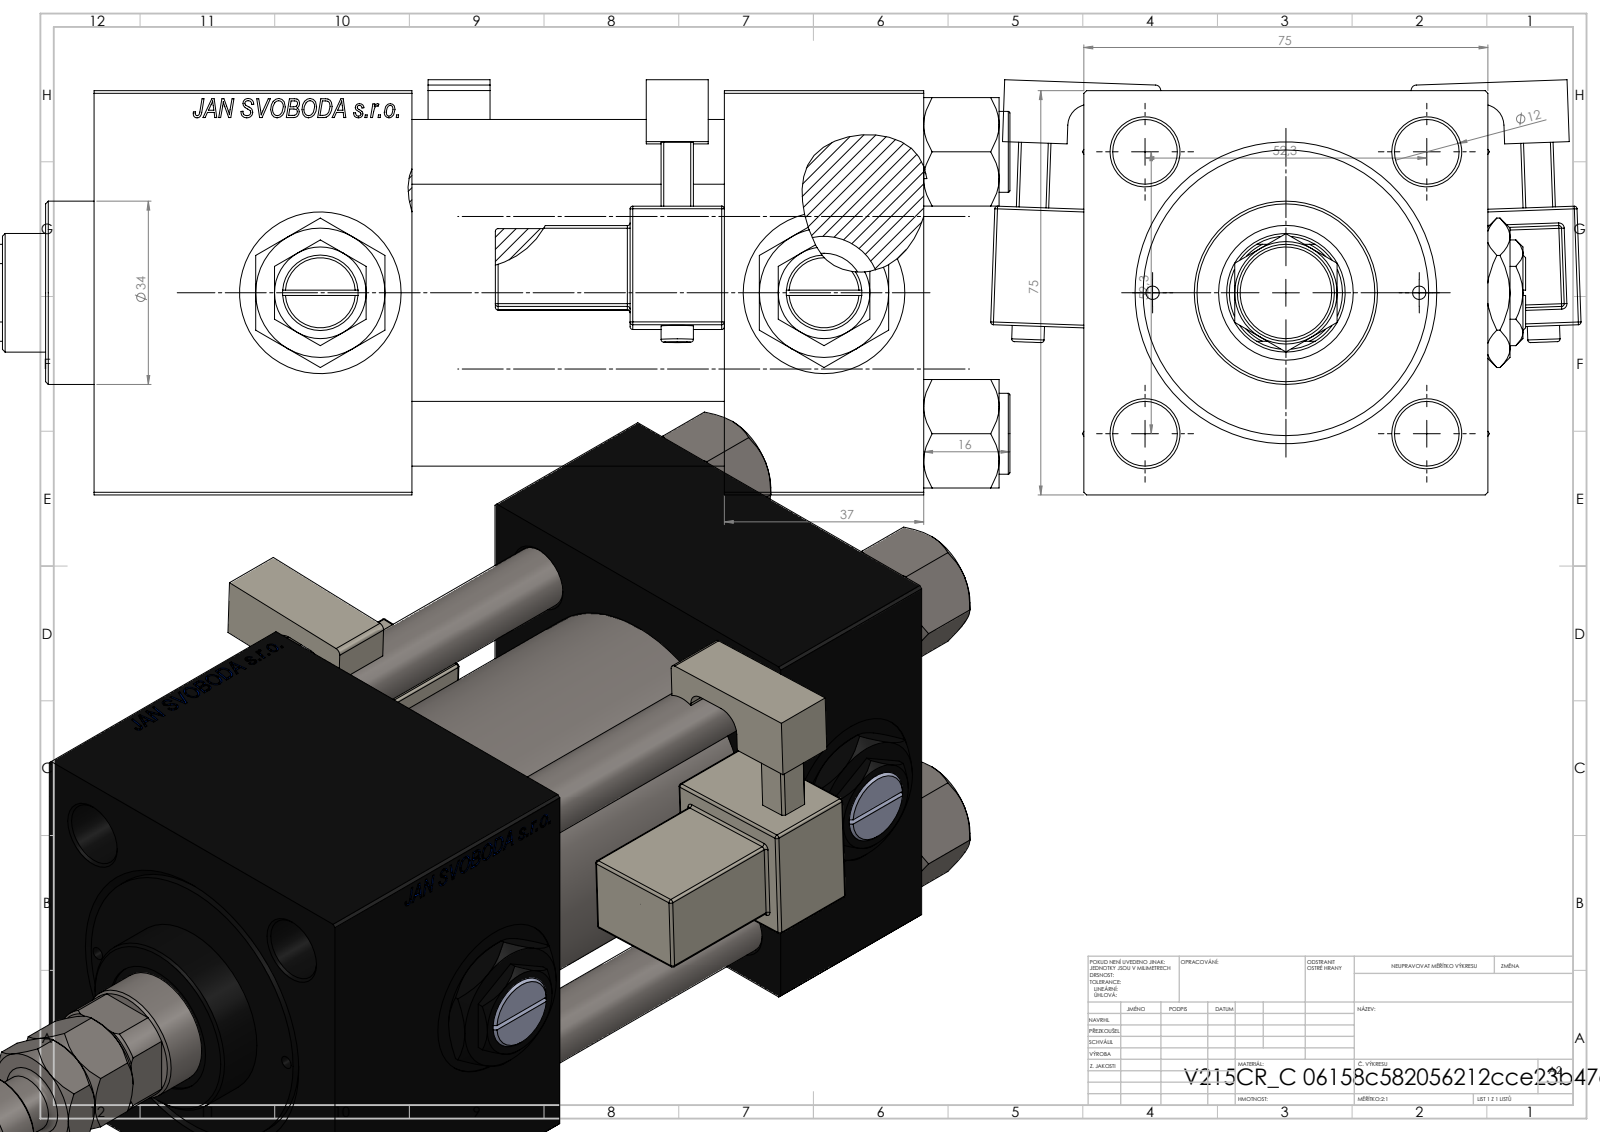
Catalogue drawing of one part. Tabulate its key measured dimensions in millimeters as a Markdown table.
| quantity | value |
| --- | --- |
| part name | MFA; V215CR_MSU; NUT_M5_C; Zatka_pro_OIL_PORT (+4 more) |
| STEP written by | SolidWorks 2019 (CONFIG_CONTROL_DESIGN) |
| units | millimeters |
| bodies | 16 solids, 1461 faces (649 planar, 166 cylindrical, 646 other) |
| overall size | 228 × 109.57 × 77.03 |
| volume | 701 003 mm³ |
| surface area | 166 807 mm² |
| round holes (diameter × count) | 12 × 4, 2.5 × 2, 7 × 2, 20.96 × 2, 30 × 2, 10.5 × 1, 22 × 1, 25 × 1, 41 × 1, 50 × 1, 53 × 1 |
| round bosses / shafts (diameter × count) | 15 × 4, 6 × 2, 56 × 1, 34 × 1, 18 × 1, 11 × 1 |
| partial cylindrical surfaces (radius × count) | 0.5 × 48, 1 × 2, 2.5 × 2, 4 × 2, 10.5 × 1 |
| main face-to-face distances | 75, 37, 117, 58, 154, 95, 59, 125.3, 88.3, 30.3 |
| hole center spacings | 26.19, 36.98, 52.3, 57.22, 24.75, 73.96, 49.5, 93.5 |
